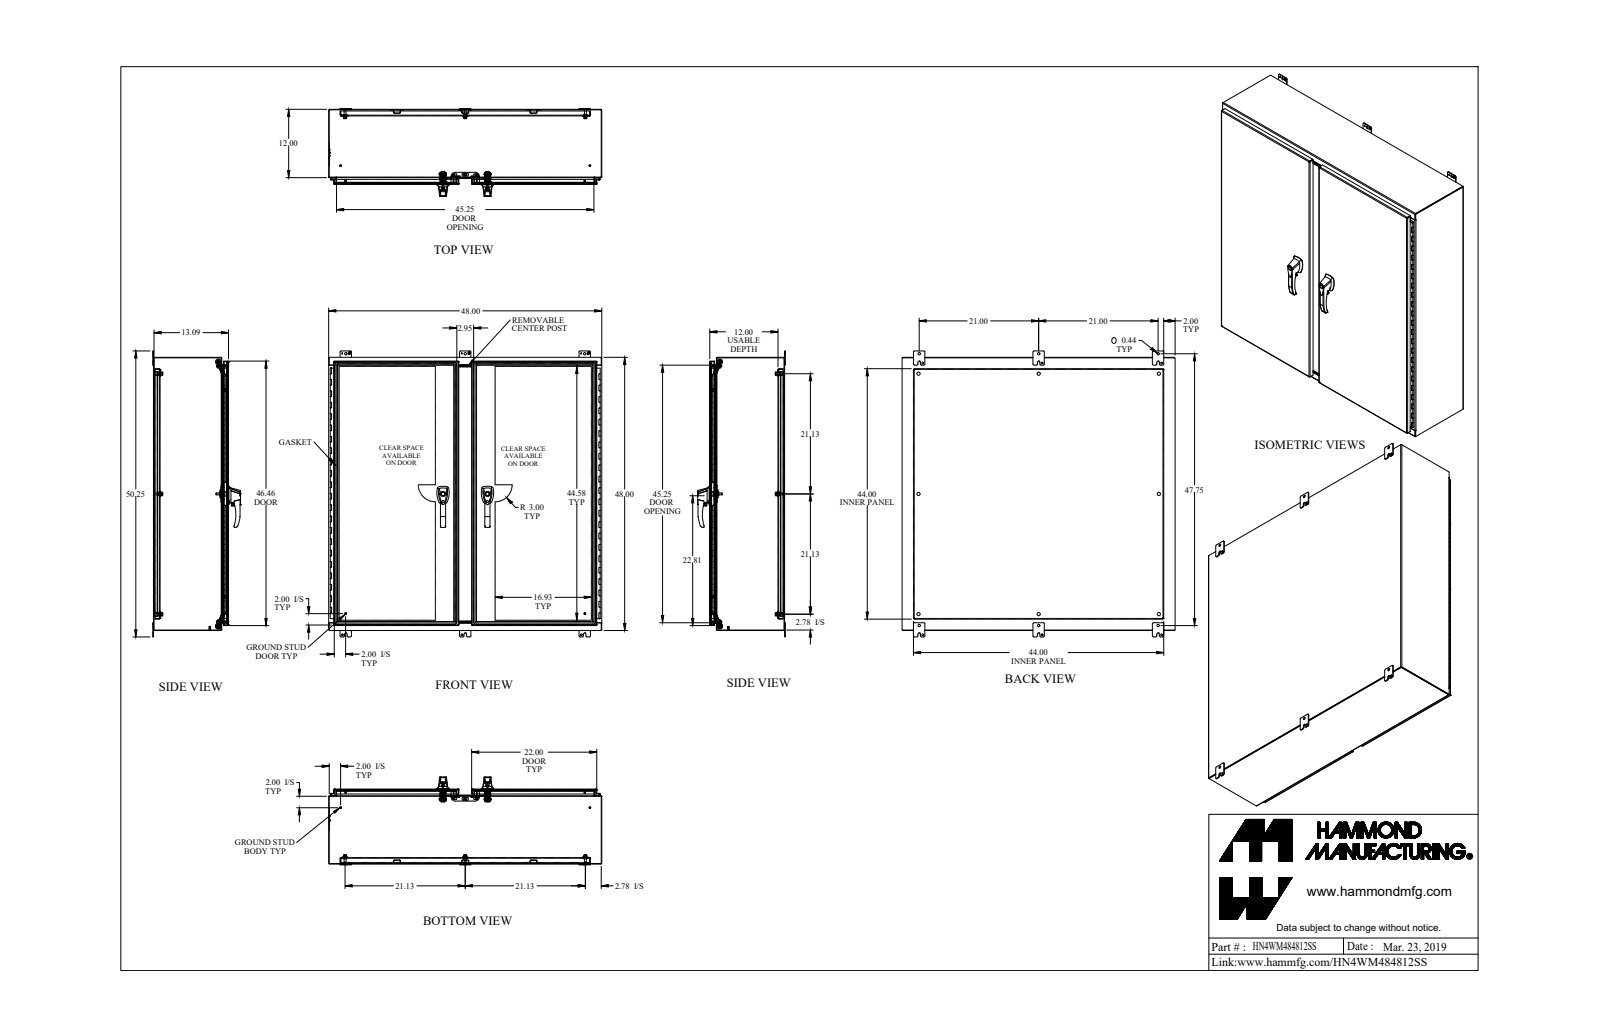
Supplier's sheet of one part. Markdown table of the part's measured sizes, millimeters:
| quantity | value |
| --- | --- |
| part name | HN4WM484812SS |
| STEP written by | SolidWorks 2018 (AUTOMOTIVE_DESIGN) |
| units | millimeters |
| bodies | 113 solids, 3230 faces (1521 planar, 1433 cylindrical, 276 other) |
| overall size | 1276.4 × 1219.2 × 391.8 |
| volume | 18 070 000 mm³ |
| surface area | 14 190 000 mm² |
| round holes (diameter × count) | 7.7 × 16, 7.8 × 8, 14.3 × 8, 8 × 6, 11.3 × 6, 6.4 × 5, 7.1 × 4, 8 × 4, 9.9 × 4, 5.1 × 3, 11.1 × 3, 2.8 × 2 |
| round bosses / shafts (diameter × count) | 25.4 × 10, 16.5 × 8, 9.5 × 8, 8.4 × 8, 19.1 × 4, 15.9 × 4, 11.2 × 4, 9.4 × 4 |
| partial cylindrical surfaces (radius × count) | 3.2 × 35, 0.5 × 32, 4.8 × 32, 6.4 × 26, 1.5 × 24, 1.2 × 17, 3.6 × 17, 12.7 × 17 |
| main face-to-face distances | 2.4, 1216.8, 2.4, 332.5, 330.1, 334.9, 332.5, 23.8, 29.4, 3.2 |
| hole center spacings | 152.4, 1181.9, 304.8, 1211, 536.6, 457.2, 1258, 1199.8 |
